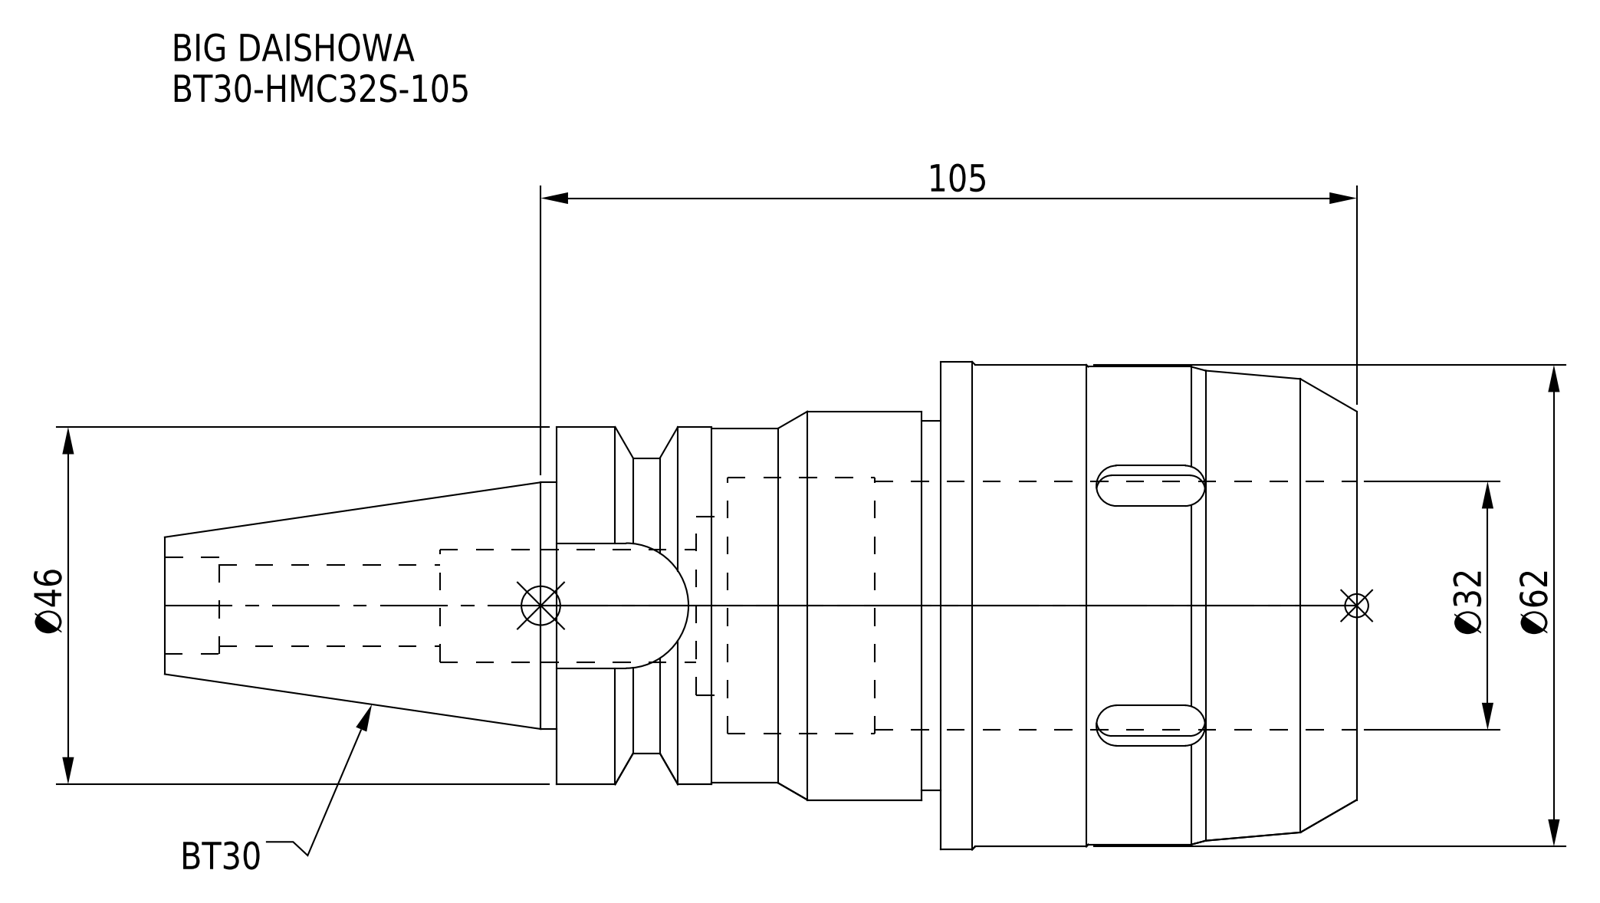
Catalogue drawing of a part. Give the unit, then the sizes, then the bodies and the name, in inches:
Units: inches
Overall size (bounding box): 6.039 × 2.472 × 2.472
Round holes (diameter × count): ⌀0.409 ×1, ⌀0.492 ×1, ⌀0.571 ×1, ⌀0.906 ×1, ⌀1.26 ×1, ⌀1.299 ×1
Round bosses / shafts (diameter × count): ⌀2.472 ×1, ⌀2.441 ×1, ⌀2.421 ×1, ⌀1.969 ×1, ⌀1.87 ×1, ⌀1.811 ×1, ⌀1.795 ×1, ⌀1.25 ×1
Partial cylindrical surfaces — rounded edges, fillets, slot ends (radius × count): R0.118 ×6, R0.317 ×1, R0.748 ×1
Main face-to-face distances: 2.106, 4.055, 1.949, 3.189, 1.083, 0.866, 3.346, 1.24, 0.157, 0.709
Volume: 11.14 in³ · Surface area: 59.72 in²
Bodies: 1 solid, 101 faces (35 planar, 48 cylindrical, 18 other)
Part name (STEP PRODUCT): BT30-HMC32S-105
STEP written by: CREO PARAMETRIC BY PTC INC, 2016380 (AUTOMOTIVE_DESIGN)
